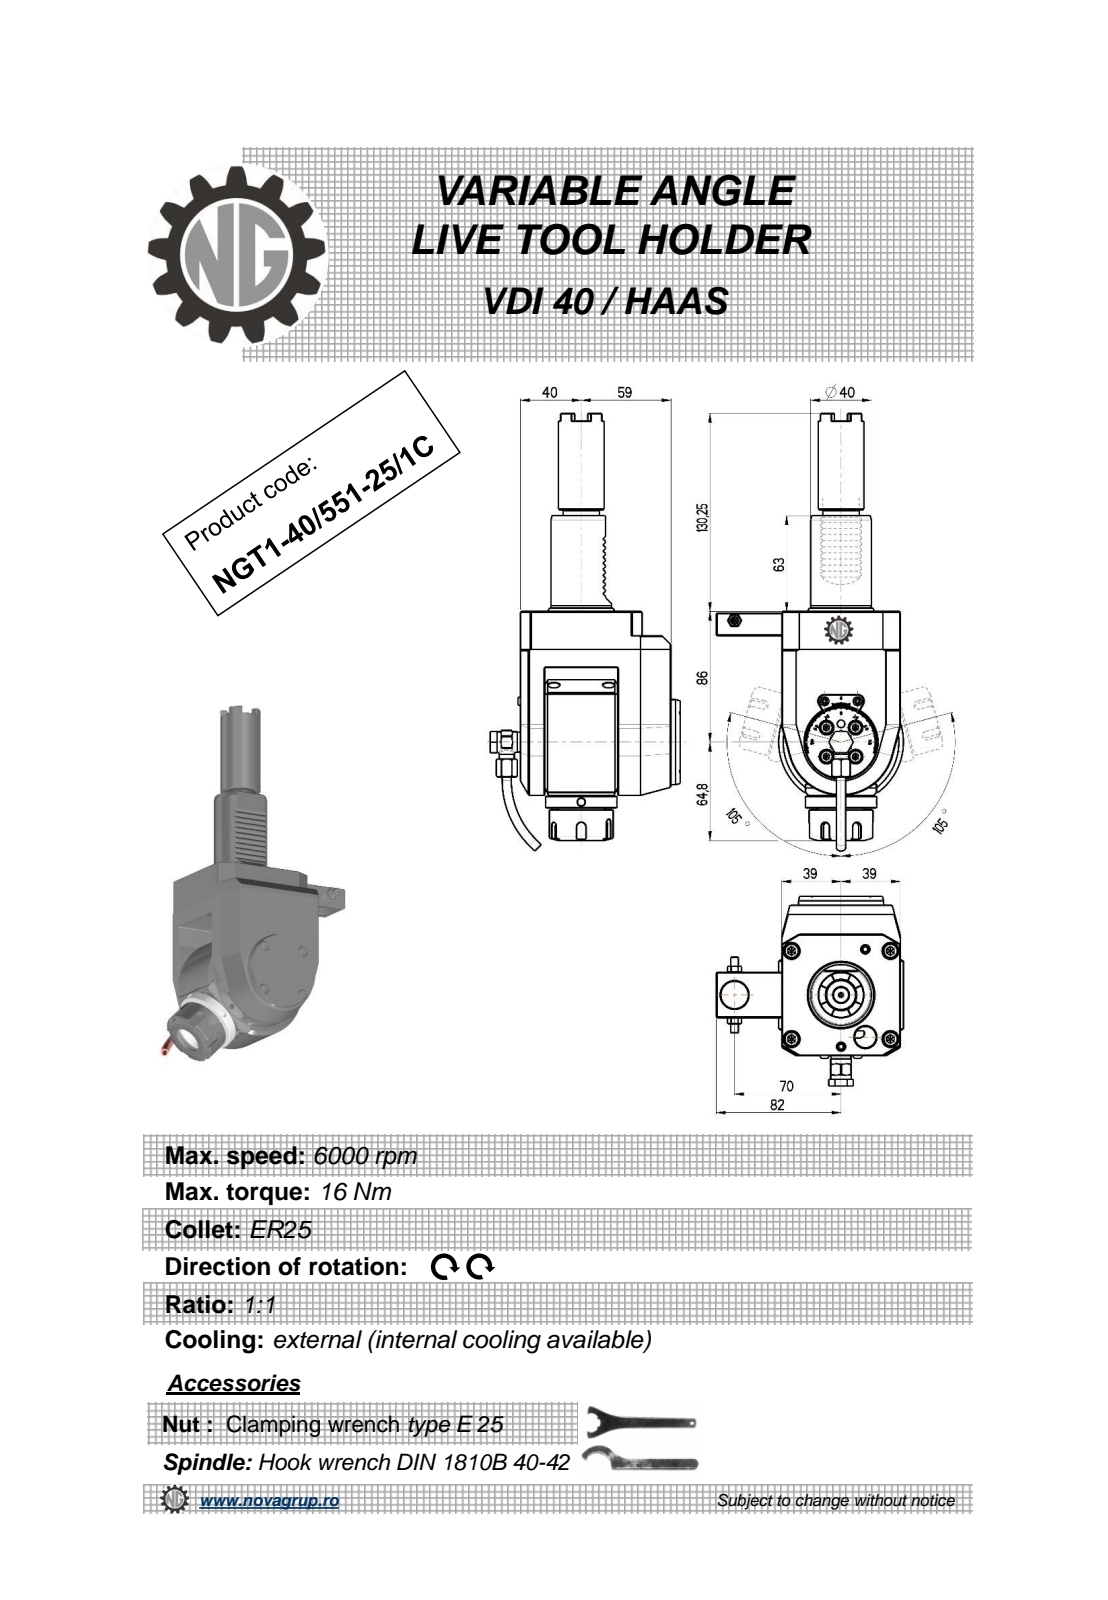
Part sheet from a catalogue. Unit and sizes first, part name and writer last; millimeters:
Units: millimetres
Overall size (bounding box): 287.92 × 124.9 × 123
Round holes (diameter × count): ⌀4 ×3, ⌀5 ×2, ⌀3 ×1, ⌀4.2 ×1, ⌀6.2 ×1, ⌀9 ×1, ⌀9.5 ×1, ⌀11 ×1, ⌀18 ×1, ⌀20.3 ×1
Round bosses / shafts (diameter × count): ⌀10 ×2, ⌀6 ×2, ⌀5.7 ×2, ⌀82 ×1, ⌀56 ×1, ⌀47 ×1, ⌀42 ×1, ⌀40 ×1
Partial cylindrical surfaces — rounded edges, fillets, slot ends (radius × count): R0.26 ×12, R0.3 ×10, R3 ×5, R0.5 ×4, R10 ×3, R1 ×2, R7.7 ×1, R35 ×1
Main face-to-face distances: 16, 37, 64, 99, 78, 6, 105, 1, 21, 25
Hole centre spacings: 0.4, 39.45, 49, 49.4, 70, 85.45, 85.68, 106.3
Volume: 968 139 mm³ · Surface area: 91 785 mm²
Bodies: 1 solid, 601 faces (266 planar, 140 cylindrical, 195 other)
Part name (STEP PRODUCT): NGT1_40_551_25_1C
STEP written by: PRO/ENGINEER BY PARAMETRIC TECHNOLOGY CORPORATION, 2010280 (CONFIG_CONTROL_DESIGN)
